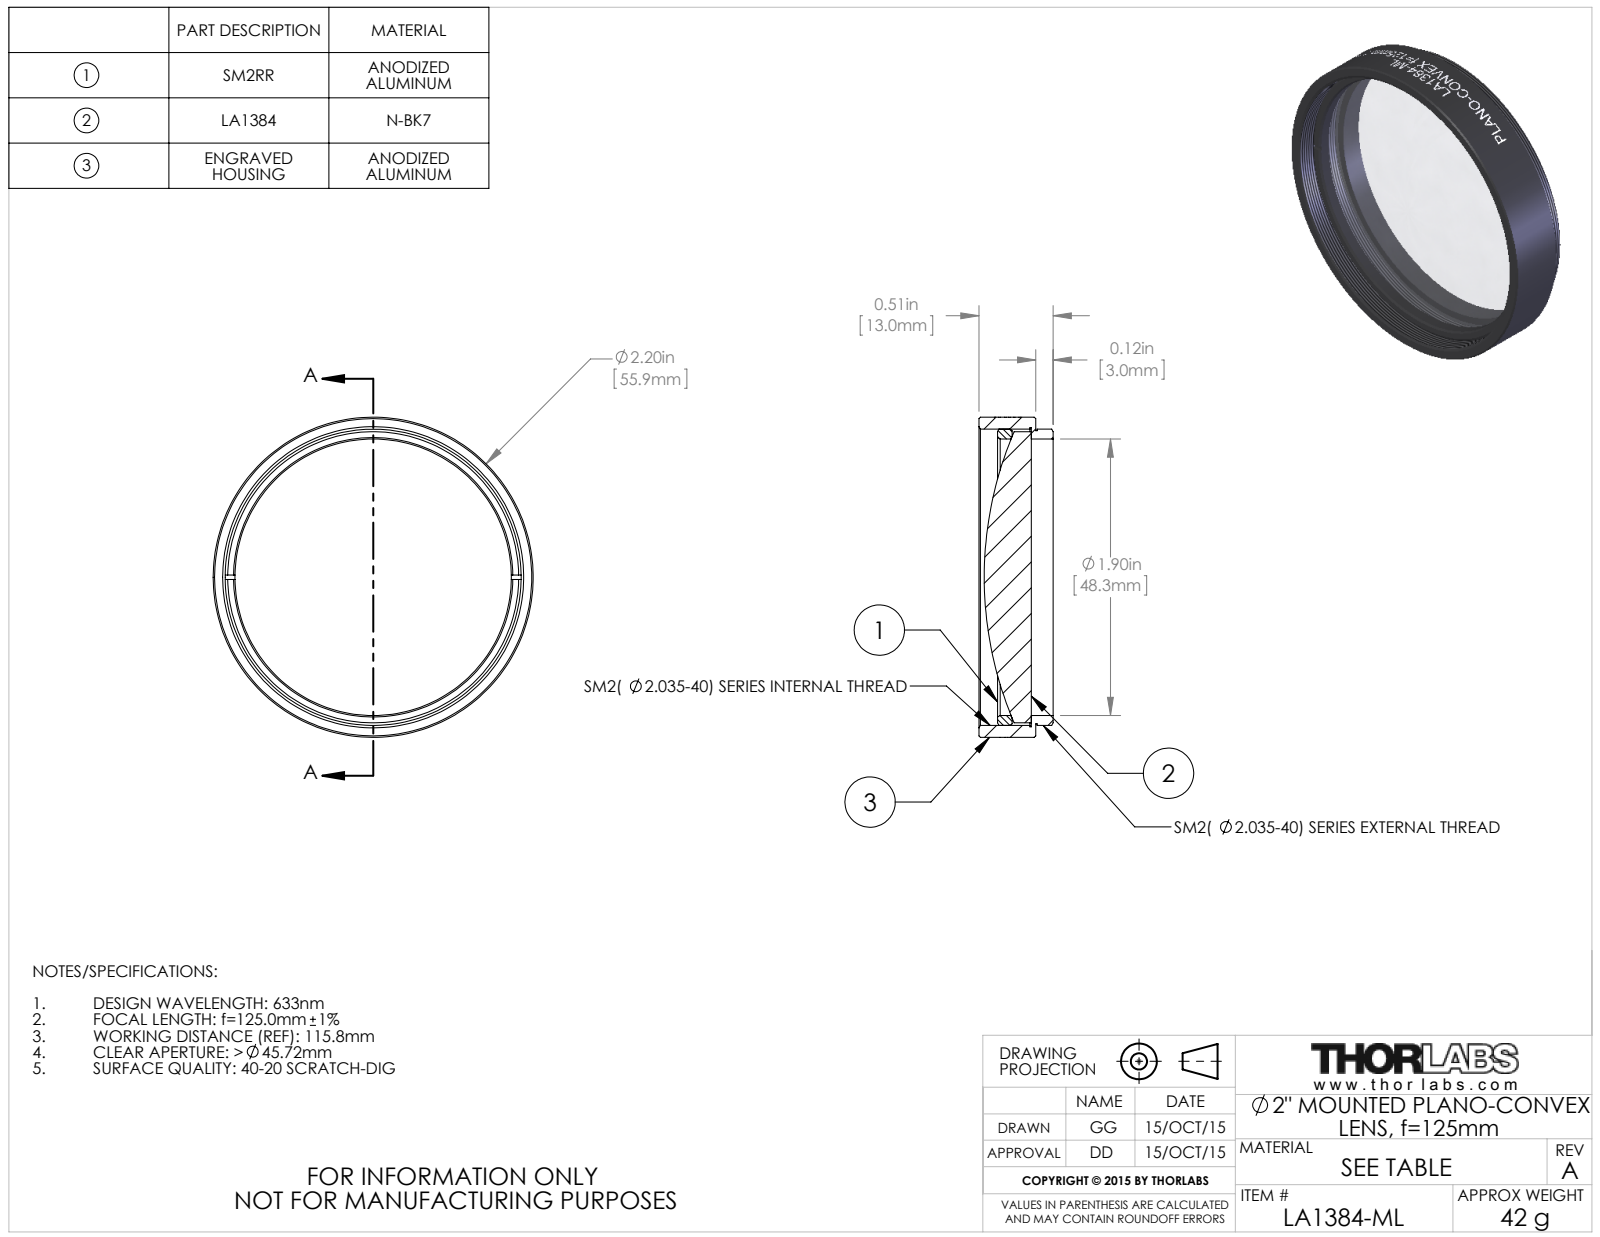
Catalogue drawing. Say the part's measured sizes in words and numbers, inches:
The part is named "TTN039570-E0W". Its 3-D file was written by "SolidWorks 2014 (CONFIG_CONTROL_DESIGN)". It is 3 solids with 108 faces: 16 planar, 72 cylindrical and 20 other. Overall it measures 2.2 by 2.2 by 0.51 inches. Its volume is 1.011 cubic inches and its surface area 17.72 square inches. Round holes: 1 of diameter 1.9, 1 of diameter 2.055. Round bosses or shafts: 1 of diameter 2.2, 1 of diameter 2.035, 1 of diameter 2.015, 1 of diameter 2. The main face-to-face distances are 0.03, 0.39, 0.36, 0.12, 0.15, 0.51, 0.282, 0.162, 0.132, 0.228.
